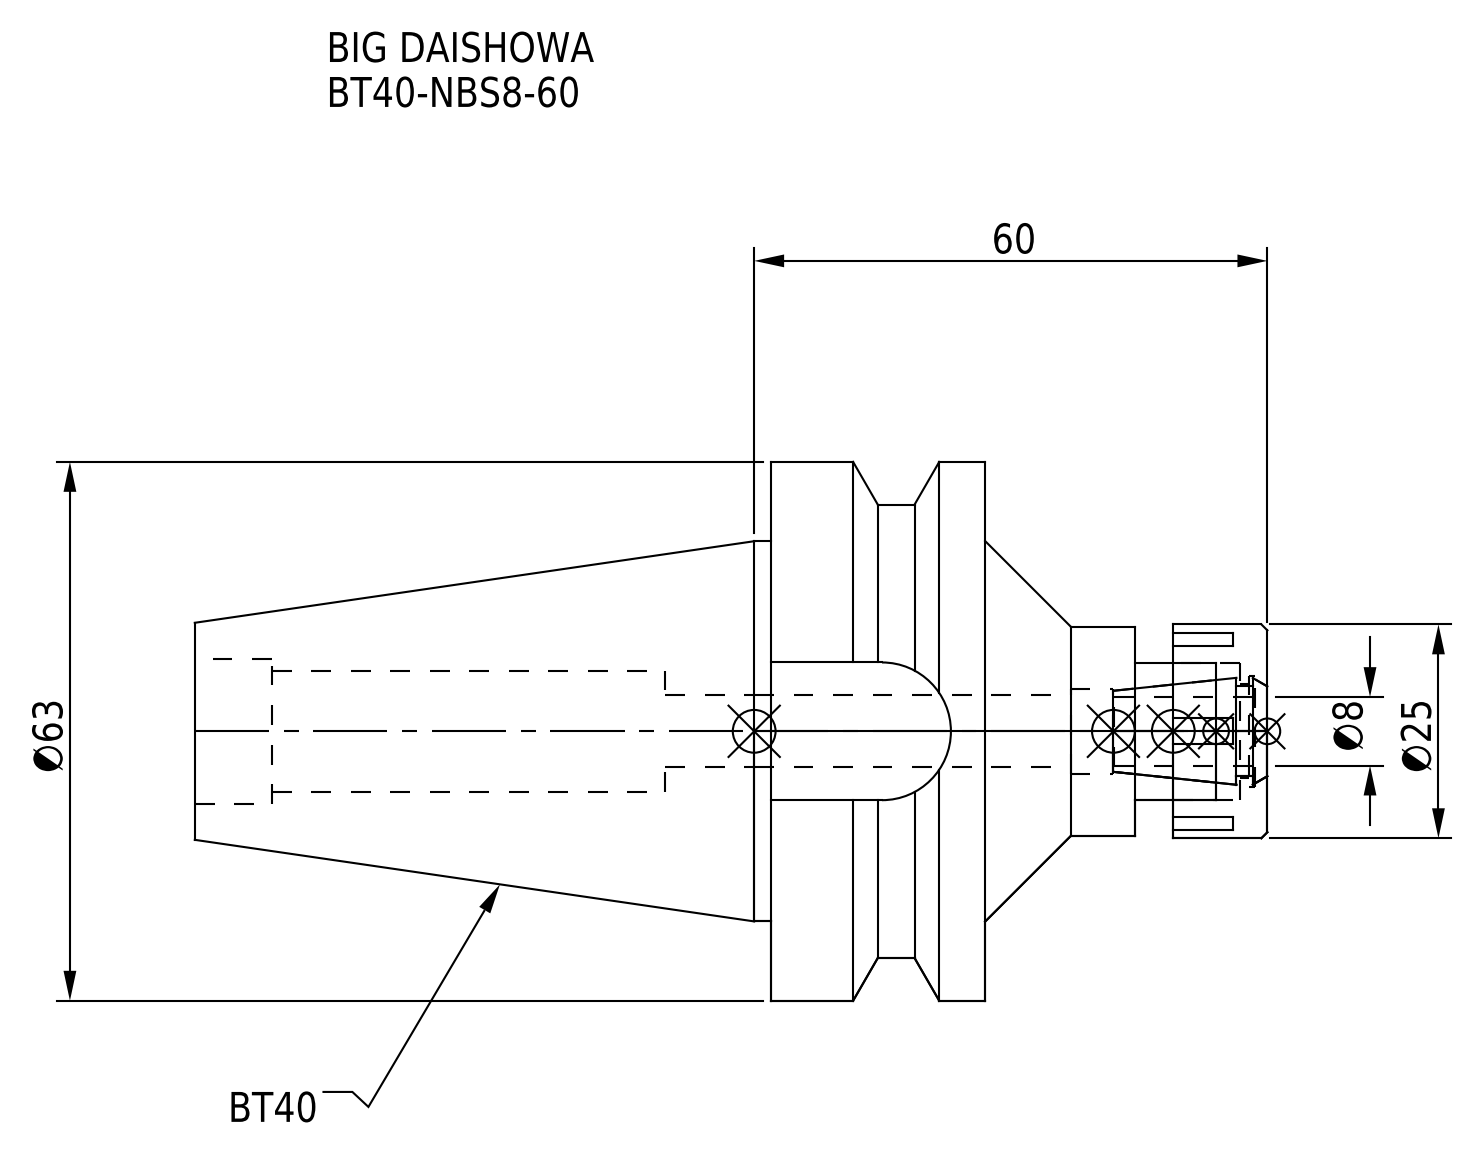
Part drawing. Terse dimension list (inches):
name: BT40-NBS8-60-FreeParts; BT40NB08060-080_ASM.stp; NBN8_1.stp; BT40-NBS8-60.stp (+3 more)
written by: SolidWorks 2019 (CONFIG_CONTROL_DESIGN)
unit: in
bodies: 2 solids, 90 faces (44 planar, 32 cylindrical, 14 other)
size: 4.937 × 2.48 × 2.48
volume: 8.494 in³; area: 41.47 in²
holes: 1× ⌀0.331, 1× ⌀0.394, 1× ⌀0.433, 1× ⌀0.512, 1× ⌀0.559, 1× ⌀0.63, 1× ⌀0.669
bosses: 1× ⌀2.48, 1× ⌀2.087, 1× ⌀1.75, 1× ⌀0.984, 1× ⌀0.965
rounds: 1× R0.317
face distances: 0.984, 1.299, 2.283, 0.866, 1.772, 4.937, 3.638, 2.654, 0.61, 0.689
